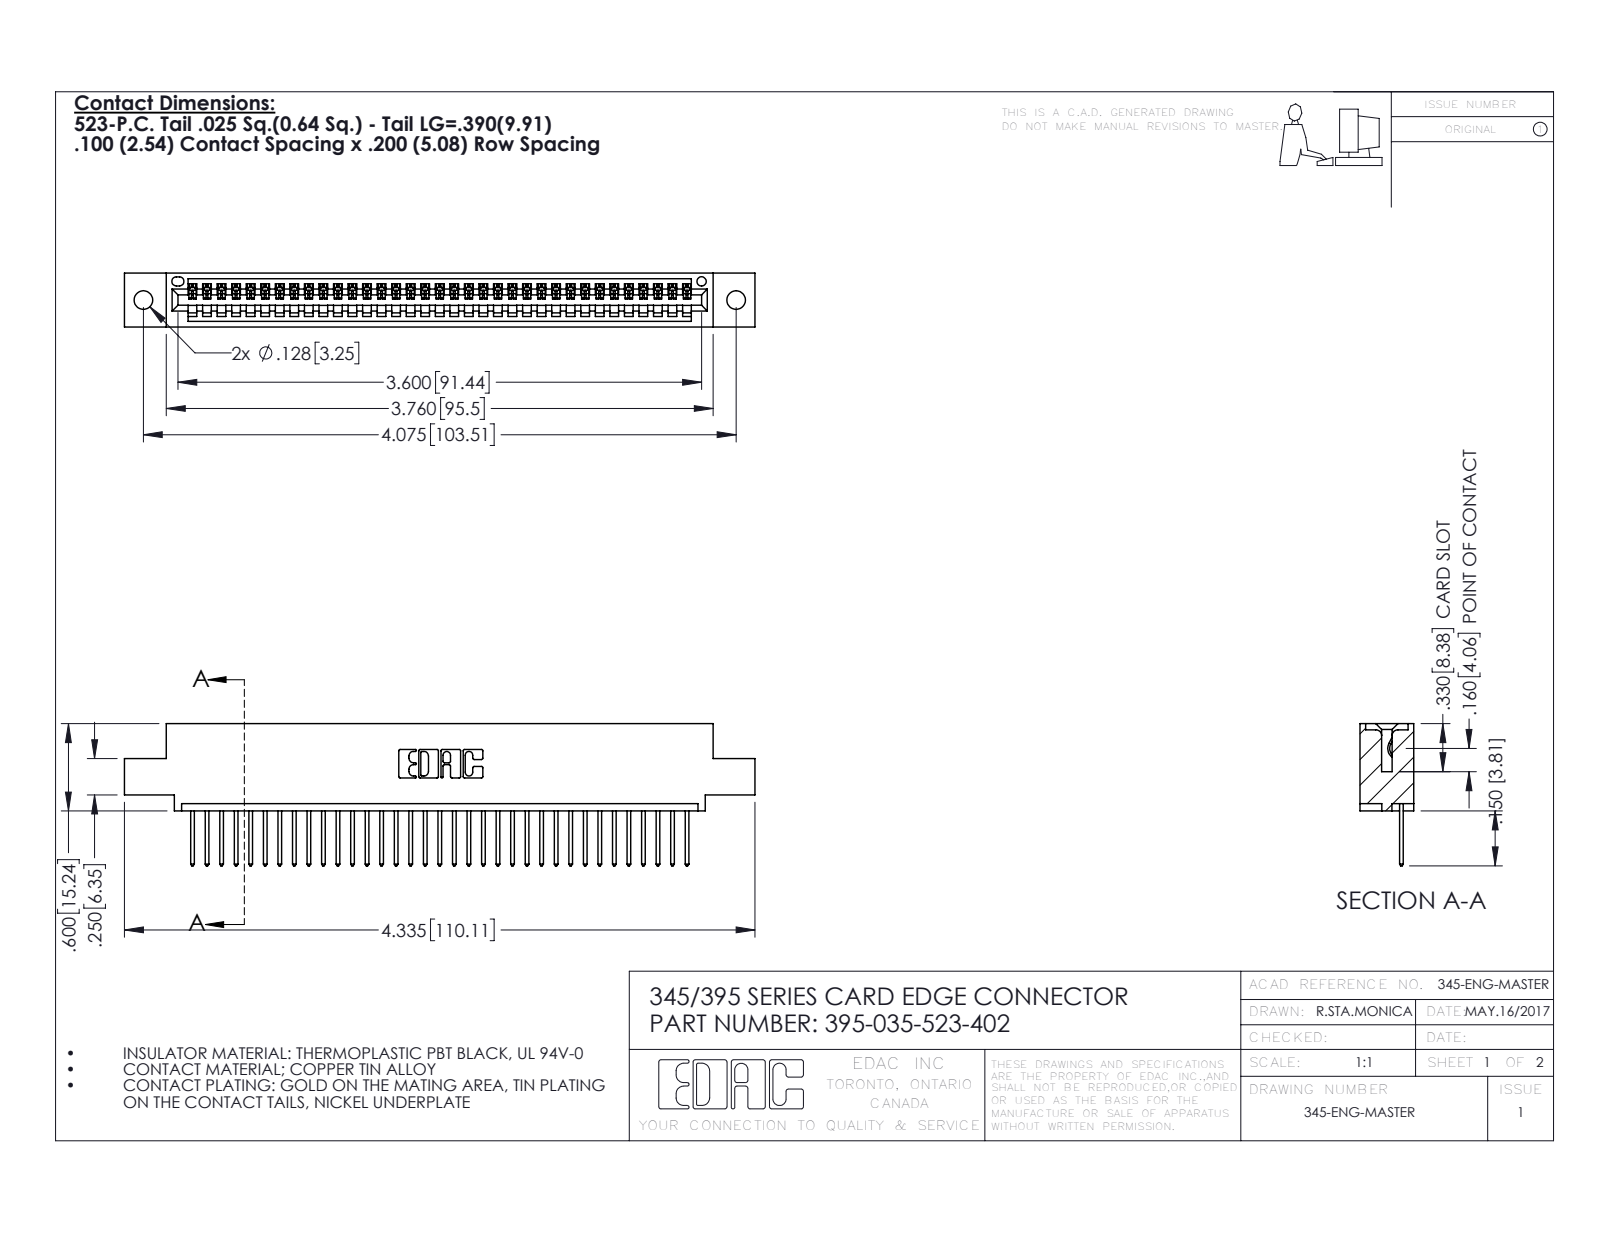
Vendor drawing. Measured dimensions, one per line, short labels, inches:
name: 345-292-001_345-293-123; 345 Part_0.110 Offset - 0.128 Dia; 395-035-523-402
written by: SolidWorks 2016 (CONFIG_CONTROL_DESIGN)
unit: in
bodies: 36 solids, 2160 faces (1484 planar, 676 cylindrical, 0 other)
size: 4.335 × 0.977 × 0.37
volume: 0.627 in³; area: 20.79 in²
holes: 2× ⌀0.128, 1× ⌀0.064
rounds: 70× R0.006, 70× R0.01, 22× R0.01, 6× R0.007, 6× R0.031, 3× R0.026, 2× R0.031, 2× R0.04
face distances: 0.298, 0.072, 0.37, 0.098, 0.272, 0.025, 0.2, 0.225, 0.149, 0.072
hole spacings: 0.27, 3.839, 4.075
